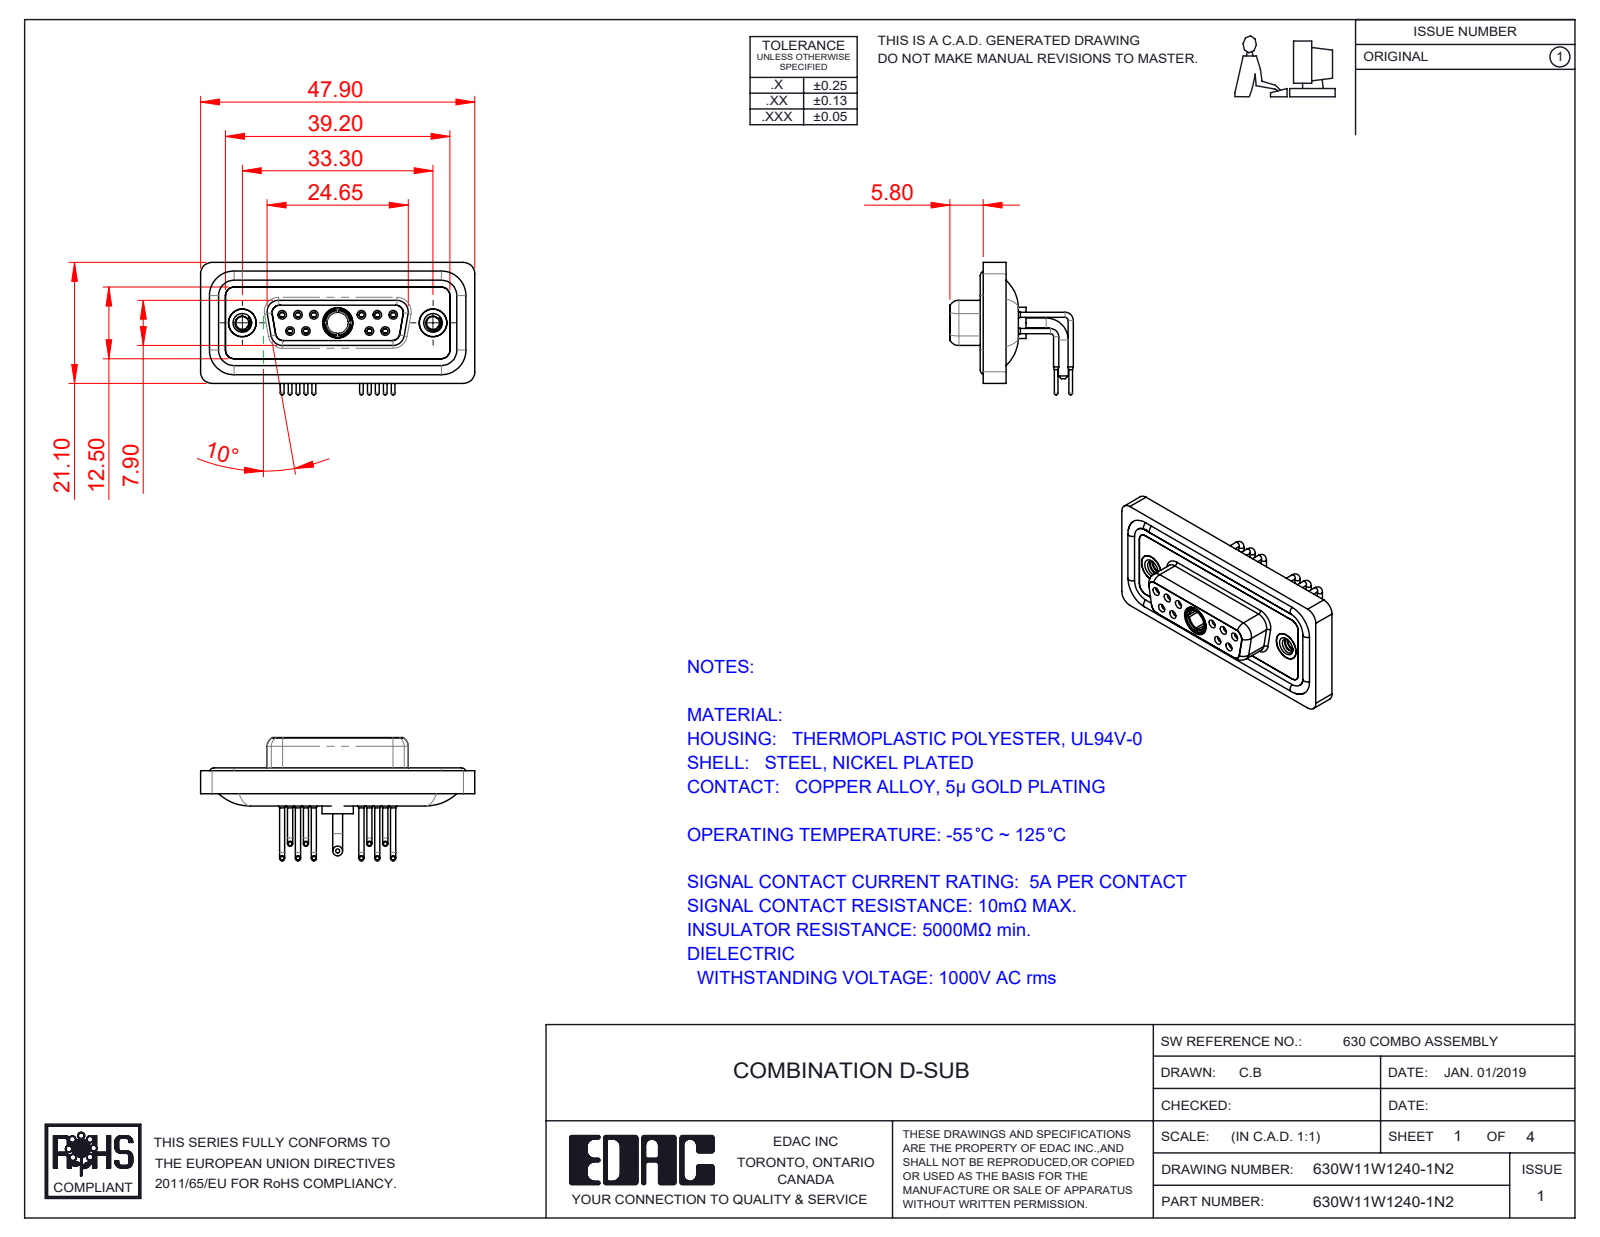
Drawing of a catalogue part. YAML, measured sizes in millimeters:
part_name: "630Combo Contact Row 2_50 Contacts; 630Combo Shell Front_15 Contacts; 630Combo Waterproof Housing_15 Contacts; 630Combo Contact Row 1_50 Contacts (+5 more)"
step_written_by: "SolidWorks 2020 (CONFIG_CONTROL_DESIGN)"
units: millimeters
bodies: {solids: 19, faces: 994, planar: 284, cylindrical: 443, other: 267}
overall_size: [47.9, 23.12, 21.53]
volume: 6160
surface_area: 10420
round_holes:
  - {diameter: 0.9, count: 10}
  - {diameter: 1.1, count: 10}
  - {diameter: 1.5, count: 10}
  - {diameter: 2, count: 10}
  - {diameter: 1.7, count: 6}
  - {diameter: 1.6, count: 4}
  - {diameter: 4.85, count: 3}
  - {diameter: 2.26, count: 2}
  - {diameter: 4, count: 2}
  - {diameter: 4.05, count: 2}
  - {diameter: 5, count: 2}
  - {diameter: 3.7, count: 1}
round_bosses_or_shafts:
  - {diameter: 1.6, count: 10}
  - {diameter: 0.9, count: 10}
  - {diameter: 0.65, count: 10}
  - {diameter: 4.95, count: 2}
  - {diameter: 4.8, count: 2}
  - {diameter: 1.7, count: 2}
  - {diameter: 5.5, count: 1}
  - {diameter: 5.2, count: 1}
partial_cylinders:
  - {radius: 2, count: 20}
  - {radius: 1.5, count: 18}
  - {radius: 1.35, count: 12}
  - {radius: 1.6, count: 8}
  - {radius: 0.25, count: 4}
  - {radius: 0.5, count: 4}
  - {radius: 0.6, count: 4}
  - {radius: 0.65, count: 4}
face_to_face_distances: [0.4, 1.8, 1.1, 1.6, 2.5, 2.9, 3.1, 3.7, 4.1, 1.5]
hole_center_spacings: [3.16, 2.77, 13.85, 11.08, 16.62, 5.03, 5.04, 5.54]
